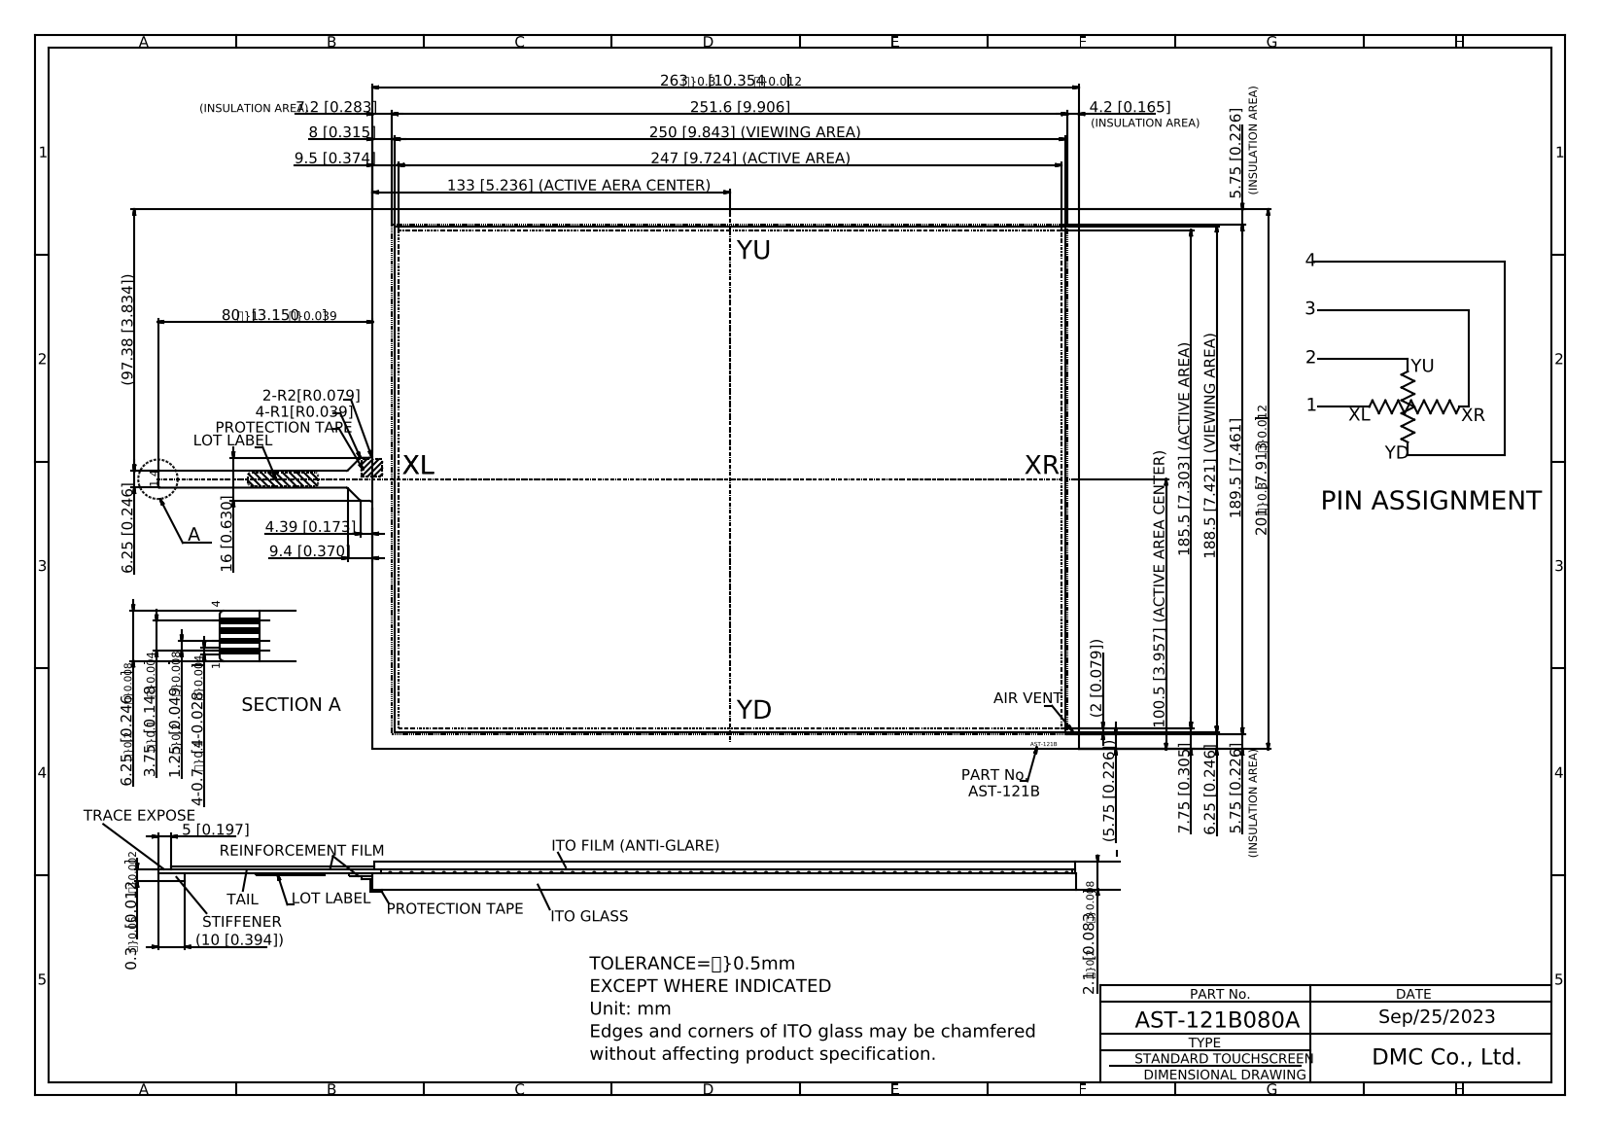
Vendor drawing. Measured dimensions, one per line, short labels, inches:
name: AST-121B080A
written by: Autodesk Inventor 2020 (CONFIG_CONTROL_DESIGN)
unit: in
bodies: 1 solid, 51 faces (45 planar, 6 cylindrical, 0 other)
size: 13.504 × 7.913 × 0.083
volume: 6.771 in³; area: 169 in²
rounds: 4× R0.039, 2× R0.02
face distances: 0.083, 0.079, 7.913, 0.075, 0.071, 10.354, 0.059, 0.016, 0.02, 0.024
